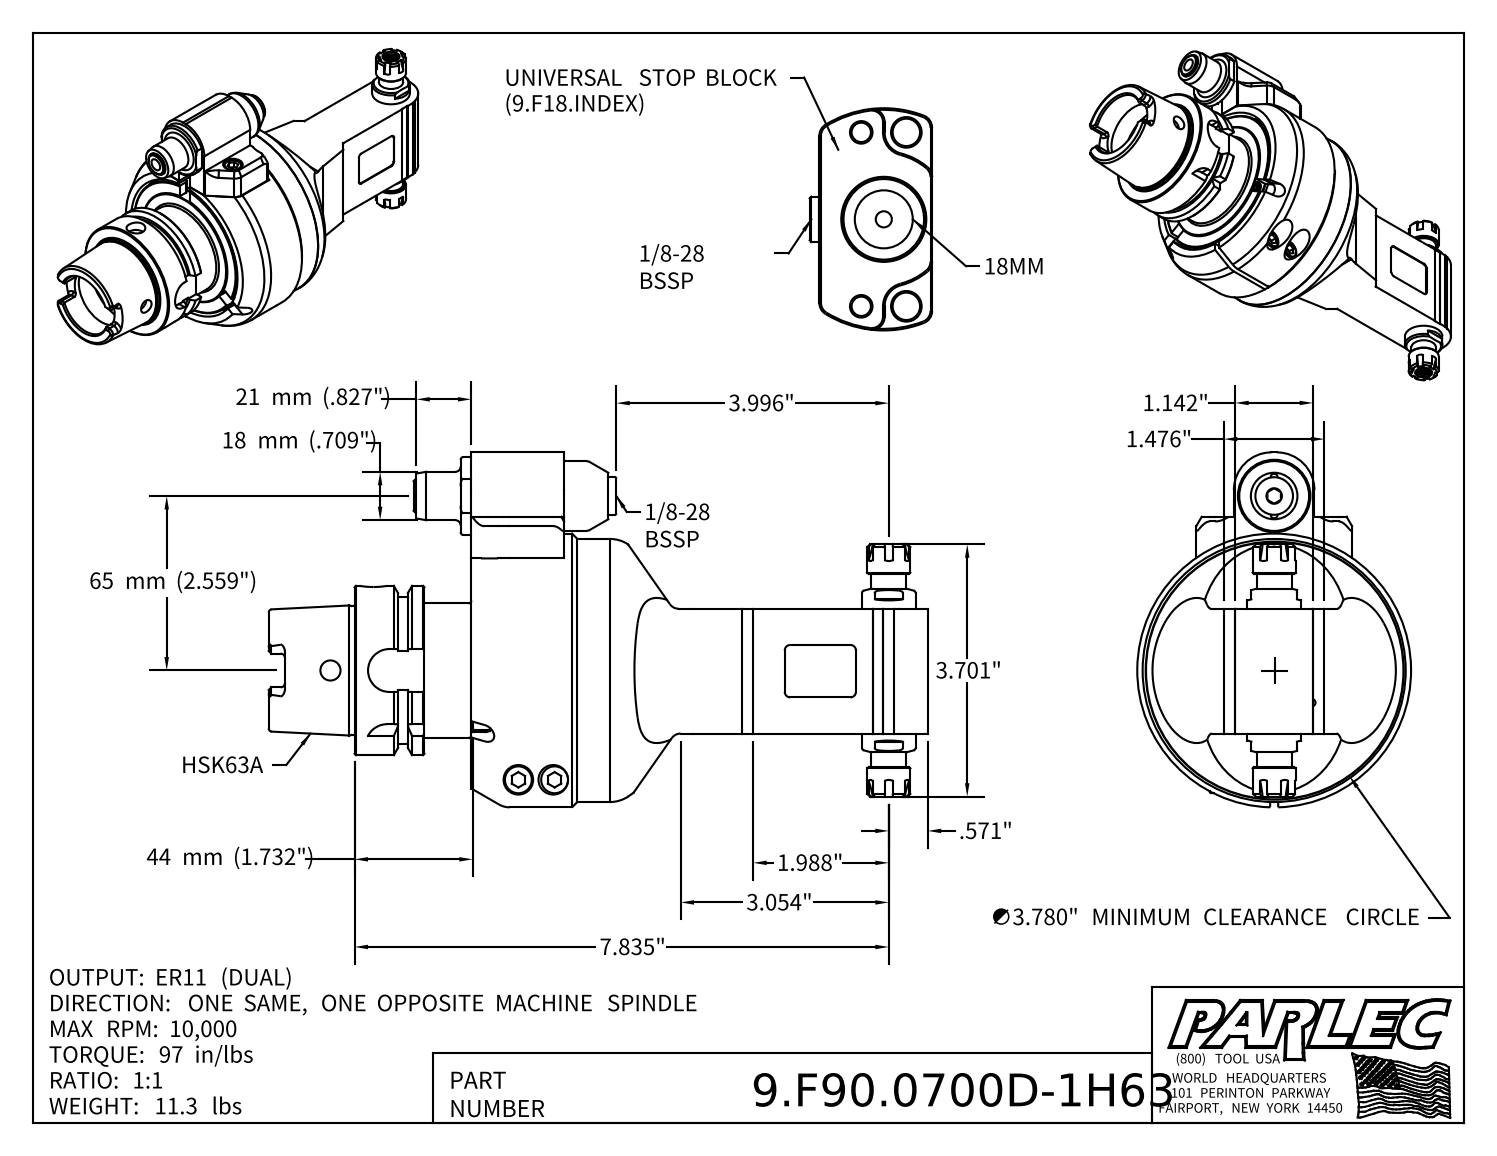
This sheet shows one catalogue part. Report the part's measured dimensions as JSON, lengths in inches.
{"part_name": "9.F90.0700D-1H63; 9_F90_07000_2U; 9_GA1_566_2 (EVO, Type 1, H63A, 65mm)", "step_written_by": "Autodesk Inventor 2022 (AUTOMOTIVE_DESIGN)", "units": "inches", "bodies": {"solids": 5, "faces": 603, "planar": 288, "cylindrical": 164, "other": 151}, "overall_size": [9.665, 5.206, 4.016], "volume_in3": 49.11, "surface_area_in2": 225.3, "round_holes": [[0.335, 21], [0.102, 2], [0.165, 2], [0.197, 2], [0.295, 2], [0.409, 2], [0.413, 2], [0.433, 2], [0.492, 2], [0.098, 1], [0.118, 1], [0.256, 1]], "round_bosses_or_shafts": [[0.394, 4], [0.236, 4], [0.709, 2], [0.315, 2], [0.098, 2], [4.016, 1], [3.85, 1], [3.031, 1]], "partial_cylinders_radius": [[0.079, 12], [1.181, 12], [0.059, 6], [0.113, 4], [0.157, 4], [0.315, 4], [0.02, 2], [0.039, 2]], "face_to_face_distances": [1.26, 0.02, 1.024, 1.831, 0.276, 0.738, 1.555, 2.569, 0.295, 1.142], "hole_center_spacings": [1.516, 1.47, 1.824, 2.144, 3.002, 0.422, 2.651, 2.914]}
